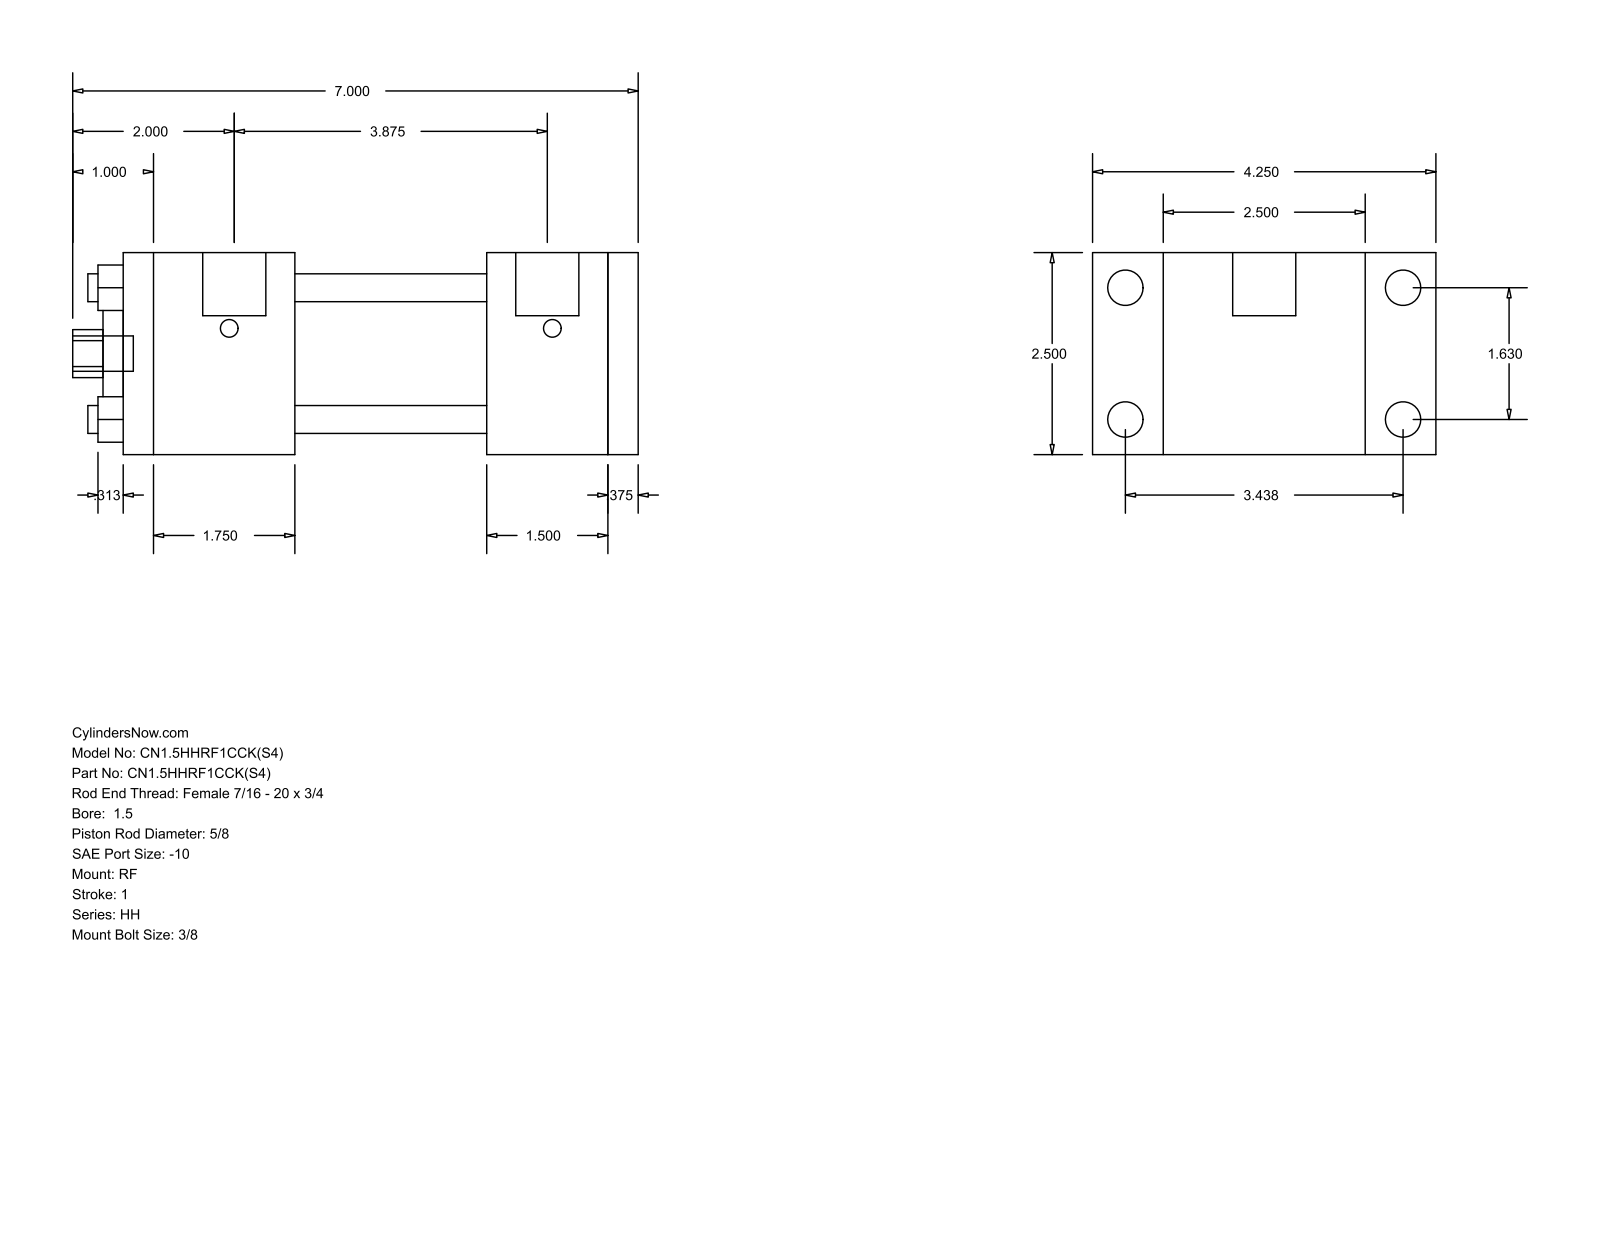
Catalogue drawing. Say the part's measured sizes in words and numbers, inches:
The part is named "HH_RF__0150_0.625". Its 3-D file was written by "GSSL Pune (CONFIG_CONTROL_DESIGN)". It is 0 solids with 92 faces: 64 planar, 28 cylindrical and 0 other. Overall it measures 7 by 4.25 by 2.5 inches. Round holes: 4 of diameter 0.345, 1 of diameter 0.625, 1 of diameter 1.125, 1 of diameter 1.75. Round bosses or shafts: 4 of diameter 0.438, 4 of diameter 0.219, 2 of diameter 0.781, 1 of diameter 0.437. Partial cylindrical surfaces (rounded edges, fillets, slot ends): 1 of radius 0.297. The main face-to-face distances are 2.5, 6.375, 0.375, 1.5, 6, 2.375, 2.125, 4.5, 3.875, 4.25. The hole center spacings are 1.152, 1.63, 2.305.
